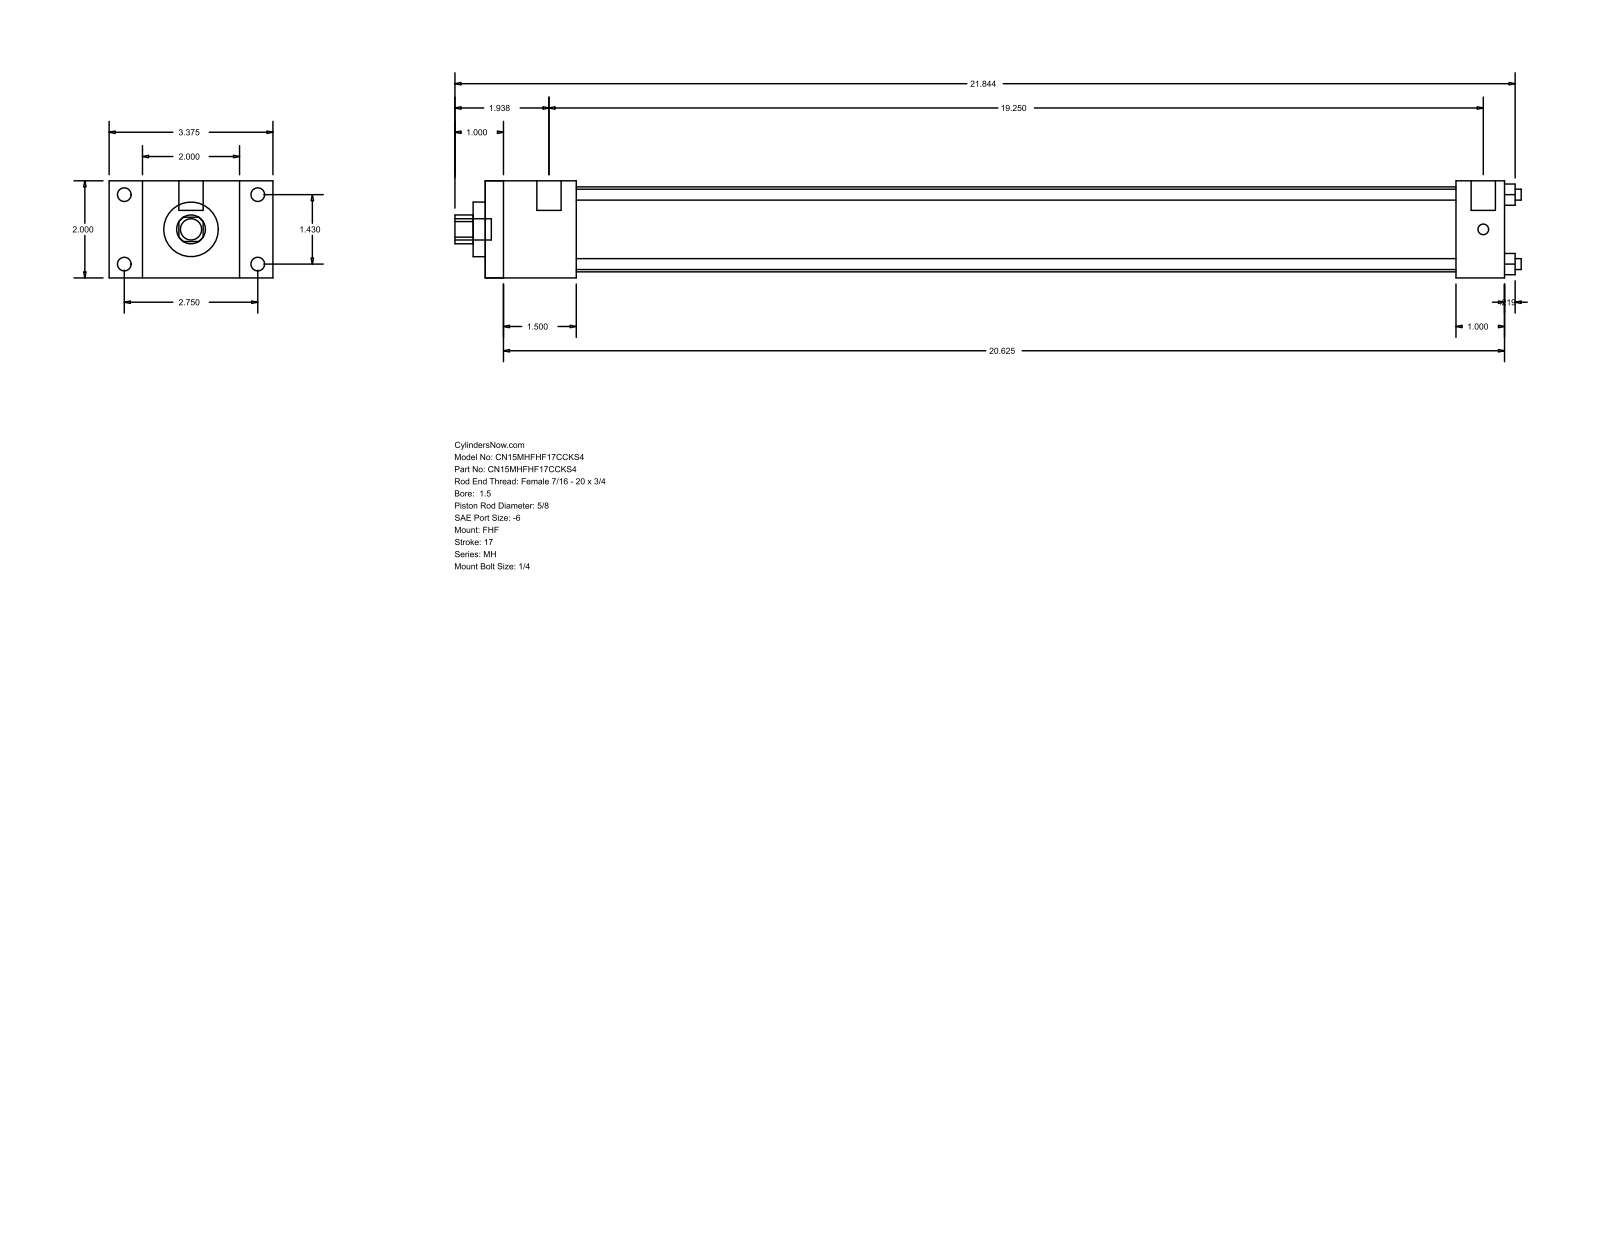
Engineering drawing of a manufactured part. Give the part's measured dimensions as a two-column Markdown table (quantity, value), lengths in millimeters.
| quantity | value |
| --- | --- |
| part name | MH_FHF__0150_0.625 |
| STEP written by | GSSL Pune (CONFIG_CONTROL_DESIGN) |
| units | millimeters |
| bodies | 0 solids, 88 faces (60 planar, 28 cylindrical, 0 other) |
| overall size | 558.01 × 85.72 × 50.8 |
| round holes (diameter × count) | 5.71 × 4, 15.88 × 1, 28.57 × 1, 44.45 × 1 |
| round bosses / shafts (diameter × count) | 7.14 × 4, 5.56 × 4, 12.7 × 2, 11.11 × 1 |
| partial cylindrical surfaces (radius × count) | 7.54 × 1 |
| main face-to-face distances | 50.8, 17.46, 68.26, 47.62, 85.72, 533.39, 485.77, 508, 460.38, 25.39 |
| hole center spacings | 25.68, 36.32, 51.36 |
